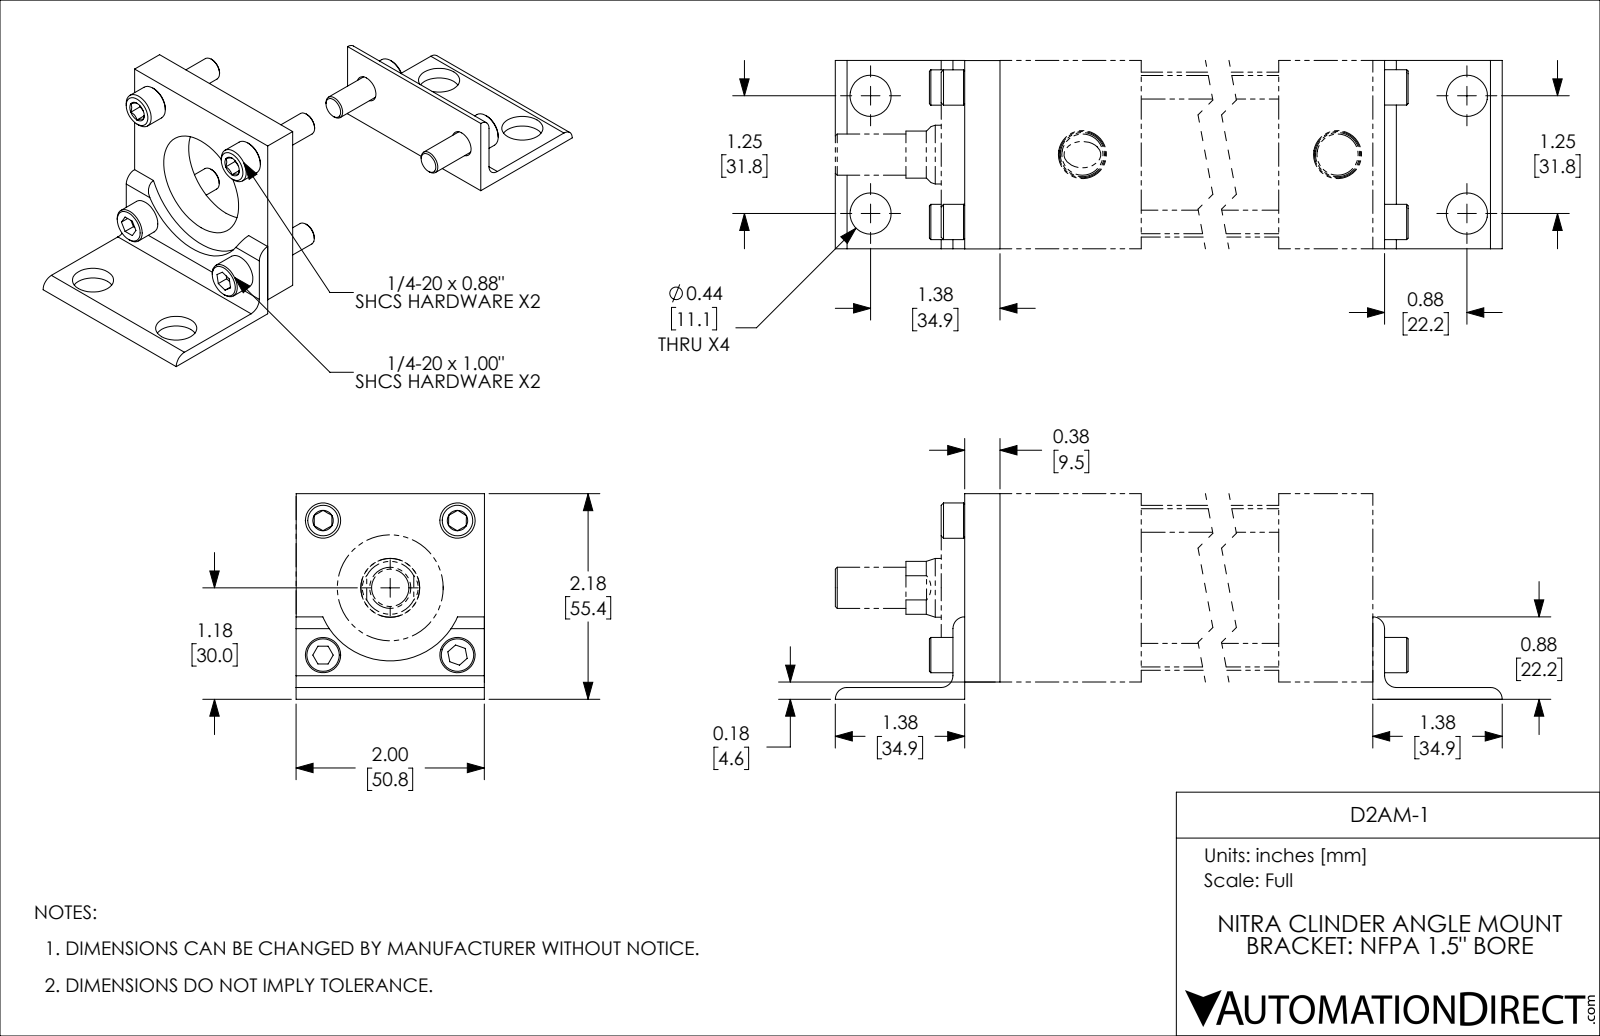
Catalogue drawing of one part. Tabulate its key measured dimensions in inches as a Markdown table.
| quantity | value |
| --- | --- |
| part name | D2AM-1_1; D2AM-1; D2AM-1_2 |
| STEP written by | SolidWorks 2019 (CONFIG_CONTROL_DESIGN) |
| units | inches |
| bodies | 9 solids, 178 faces (78 planar, 58 cylindrical, 42 other) |
| overall size | 8.75 × 2.183 × 2.001 |
| volume | 2.306 in³ |
| surface area | 35.54 in² |
| round holes (diameter × count) | 0.281 × 5, 0.437 × 4, 1.126 × 1 |
| round bosses / shafts (diameter × count) | 0.25 × 5, 0.375 × 4, 0.375 × 2 |
| partial cylindrical surfaces (radius × count) | 0.125 × 6, 0.781 × 1 |
| main face-to-face distances | 0.125, 0.375, 2, 5.625, 6.125, 6, 5.75, 0.5, 6.25, 2.058 |
| hole center spacings | 1.428, 1.01, 1.25, 2.02, 1.011, 1.43, 2.021, 8 |
